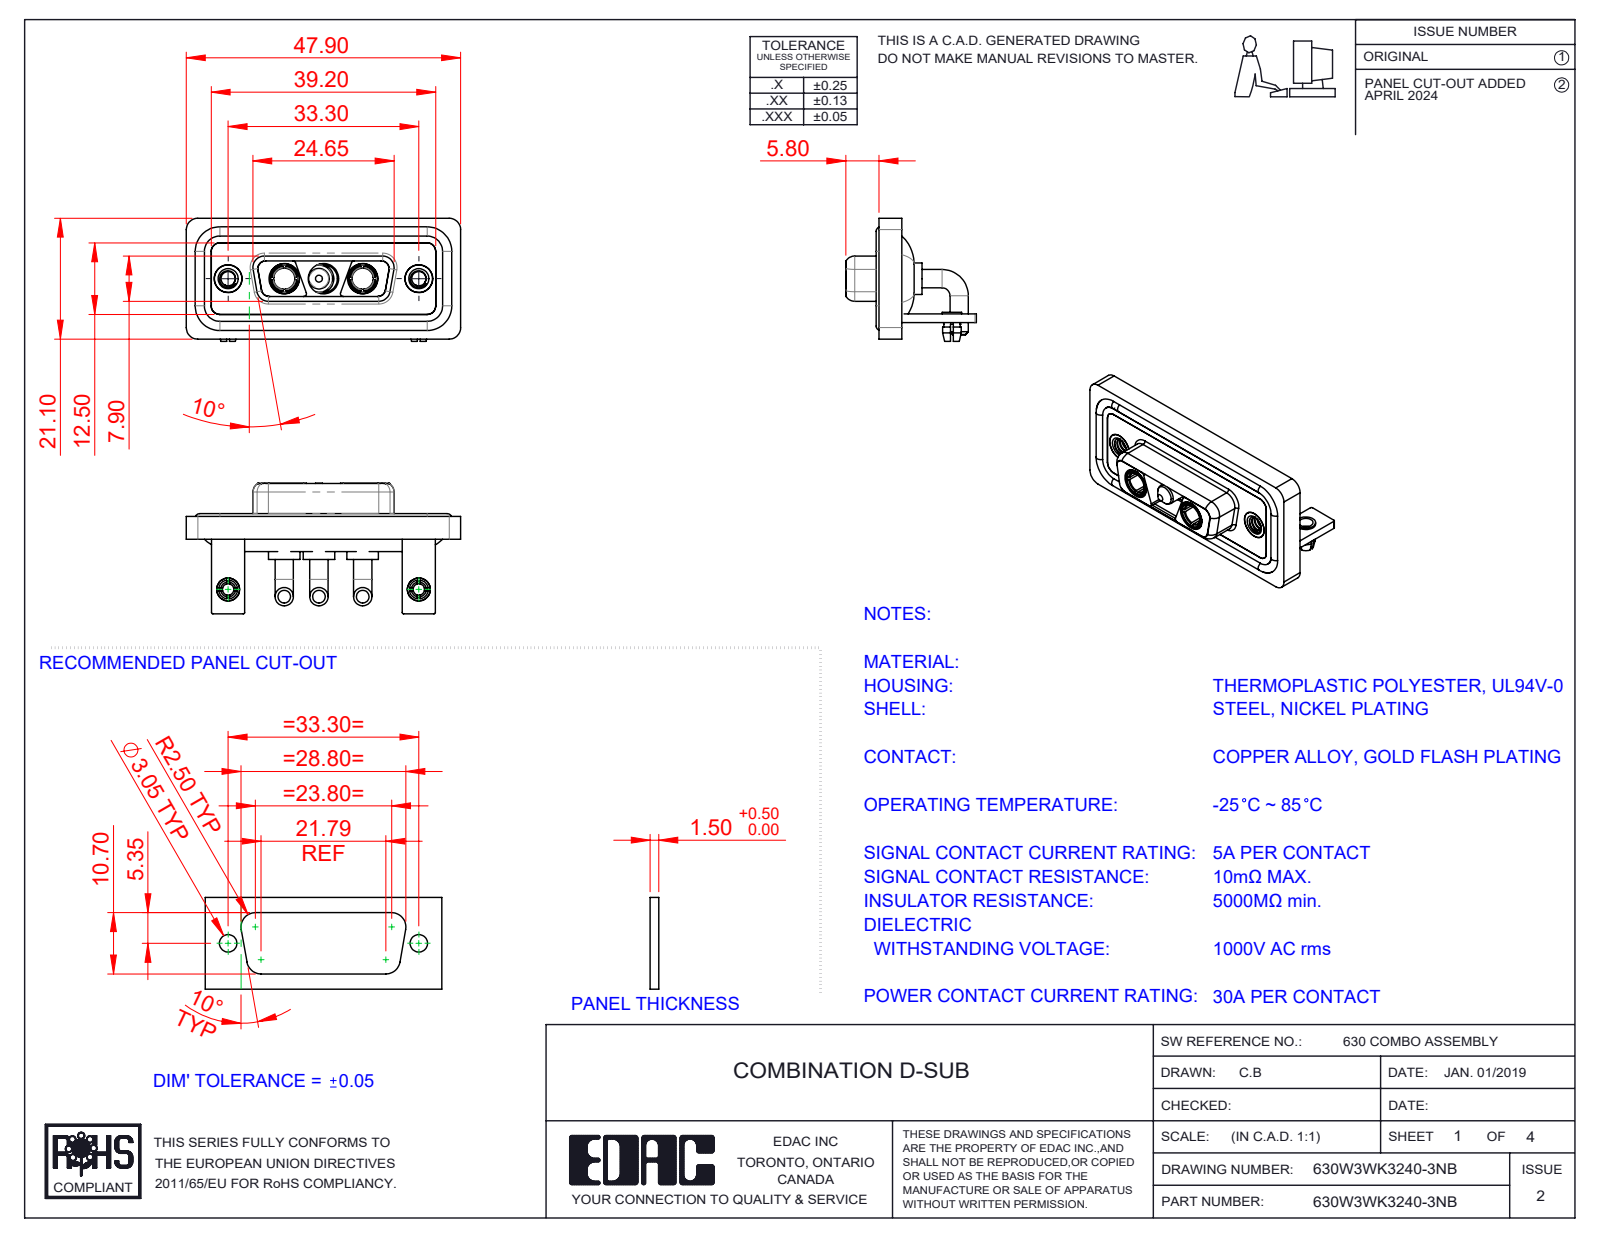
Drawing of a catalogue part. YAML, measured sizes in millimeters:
part_name: "630W3WK3140-3NB; 630Combo Threaded Rivet_A; 630Combo Board Lock_50 Contacts; 630Combo Stabilizer Bracket_50 Contacts (+6 more)"
step_written_by: "SolidWorks 2023 (CONFIG_CONTROL_DESIGN)"
units: millimeters
bodies: {solids: 17, faces: 729, planar: 246, cylindrical: 318, other: 165}
overall_size: [47.9, 22.8, 21.5]
volume: 6512
surface_area: 10743
round_holes:
  - {diameter: 4.85, count: 5}
  - {diameter: 2.5, count: 4}
  - {diameter: 5.3, count: 3}
  - {diameter: 2, count: 2}
  - {diameter: 3.2, count: 2}
  - {diameter: 3.7, count: 2}
  - {diameter: 4, count: 2}
  - {diameter: 4.05, count: 2}
  - {diameter: 5, count: 2}
round_bosses_or_shafts:
  - {diameter: 3.2, count: 6}
  - {diameter: 1.6, count: 4}
  - {diameter: 5.5, count: 3}
  - {diameter: 5.2, count: 3}
  - {diameter: 4.75, count: 3}
  - {diameter: 3.75, count: 3}
  - {diameter: 4.96, count: 2}
  - {diameter: 4.95, count: 2}
partial_cylinders:
  - {radius: 2, count: 21}
  - {radius: 1.5, count: 18}
  - {radius: 0.25, count: 16}
  - {radius: 1.35, count: 12}
  - {radius: 0.5, count: 9}
  - {radius: 1.6, count: 8}
  - {radius: 0.6, count: 4}
  - {radius: 0.65, count: 4}
face_to_face_distances: [0.4, 2.9, 1.5, 3.7, 1.8, 1.1, 4.1, 1.6, 2.5, 1.4]
hole_center_spacings: [6.85, 9.8, 16.65, 23.5, 33.3, 13.7]
